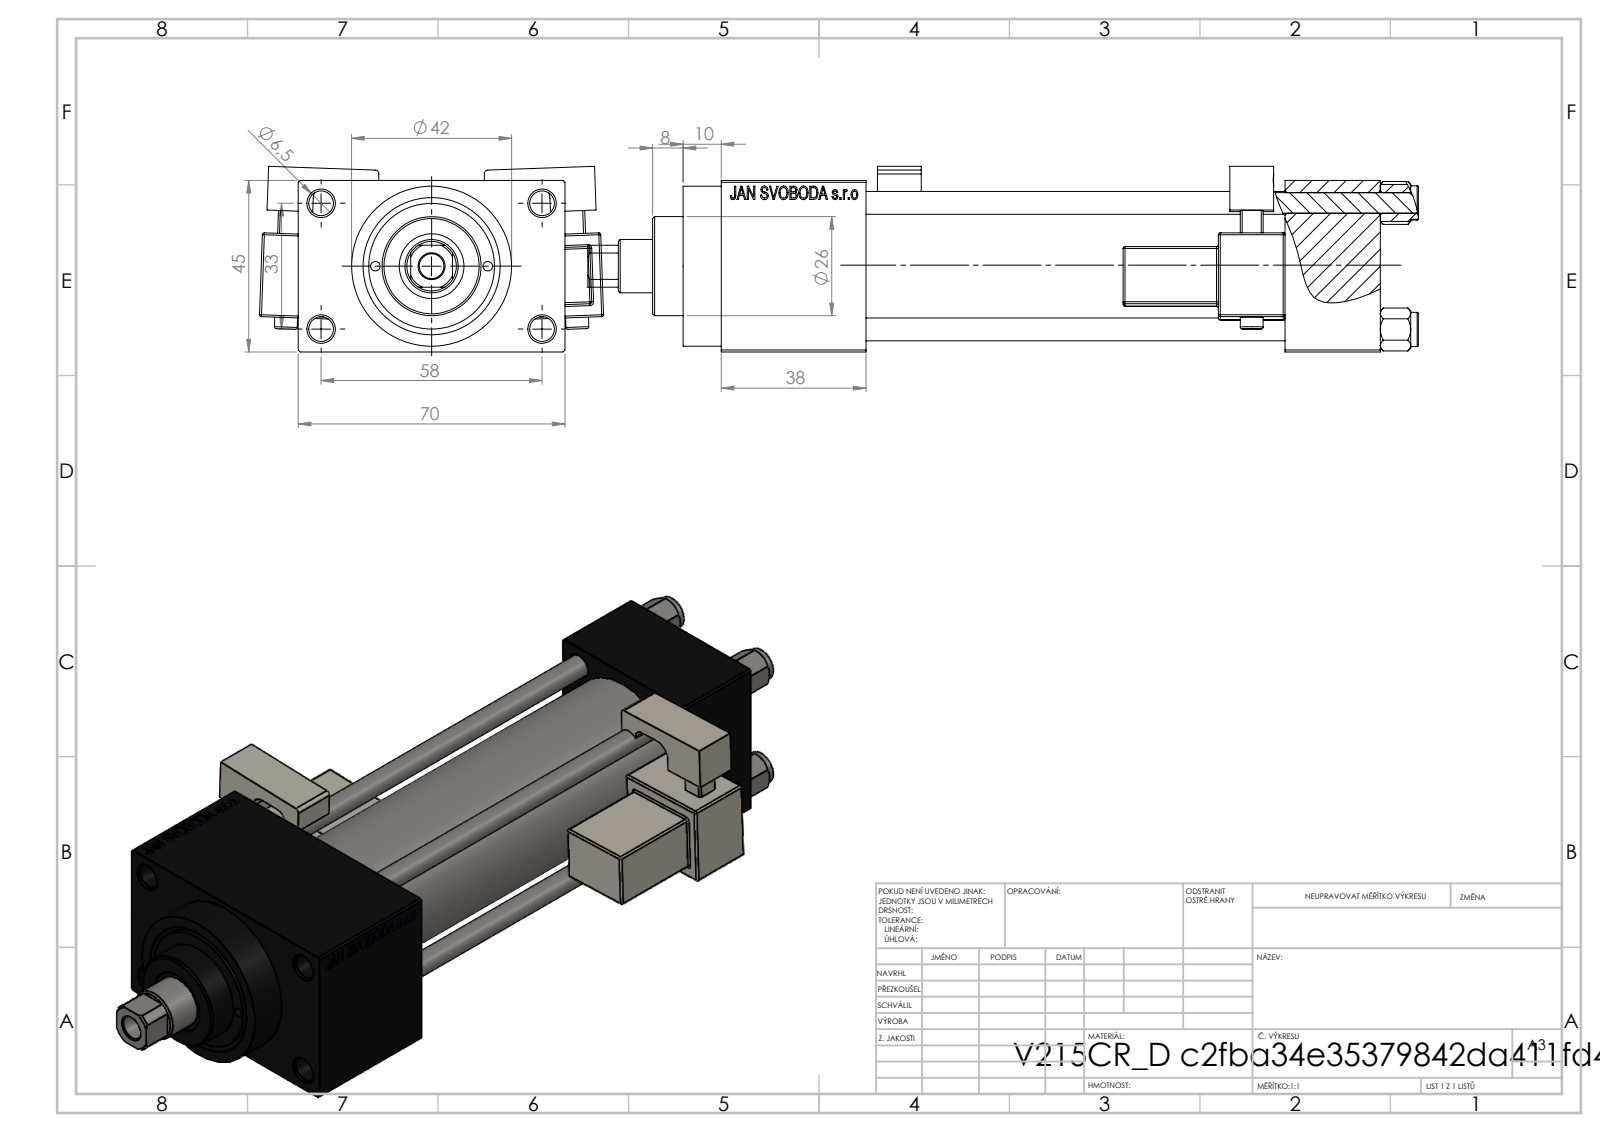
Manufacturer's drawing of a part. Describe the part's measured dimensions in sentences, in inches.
The part is named "V215_VC_A; V215CR_VCP_D; NUT_M5_D; V215CR_MSU (+2 more)". Its 3-D file was written by "SolidWorks 2019 (CONFIG_CONTROL_DESIGN)". It is 13 solids with 1268 faces: 560 planar, 152 cylindrical and 556 other. Overall it measures 8.583 by 3.556 by 1.918 inches. Its volume is 18.71 cubic inches and its surface area 167 square inches. Round holes: 5 of diameter 0.256, 4 of diameter 0.236, 2 of diameter 0.098, 2 of diameter 0.276, 2 of diameter 0.518, 2 of diameter 0.787, 1 of diameter 0.551, 1 of diameter 0.669, 1 of diameter 0.945, 1 of diameter 1.26, 1 of diameter 1.299. Round bosses or shafts: 4 of diameter 0.354, 2 of diameter 0.236, 1 of diameter 1.654, 1 of diameter 1.496, 1 of diameter 1.024. Partial cylindrical surfaces (rounded edges, fillets, slot ends): 48 of radius 0.02, 2 of radius 0.039, 2 of radius 0.098, 2 of radius 0.157, 1 of radius 0.256. The main face-to-face distances are 1.772, 0.984, 4.331, 0.492, 0.118, 5.315, 2.264, 5.827, 1.496, 6.811. The hole center spacings are 0.488, 0.657, 0.858, 0.924, 1.307, 1.314, 1.392, 1.396.
